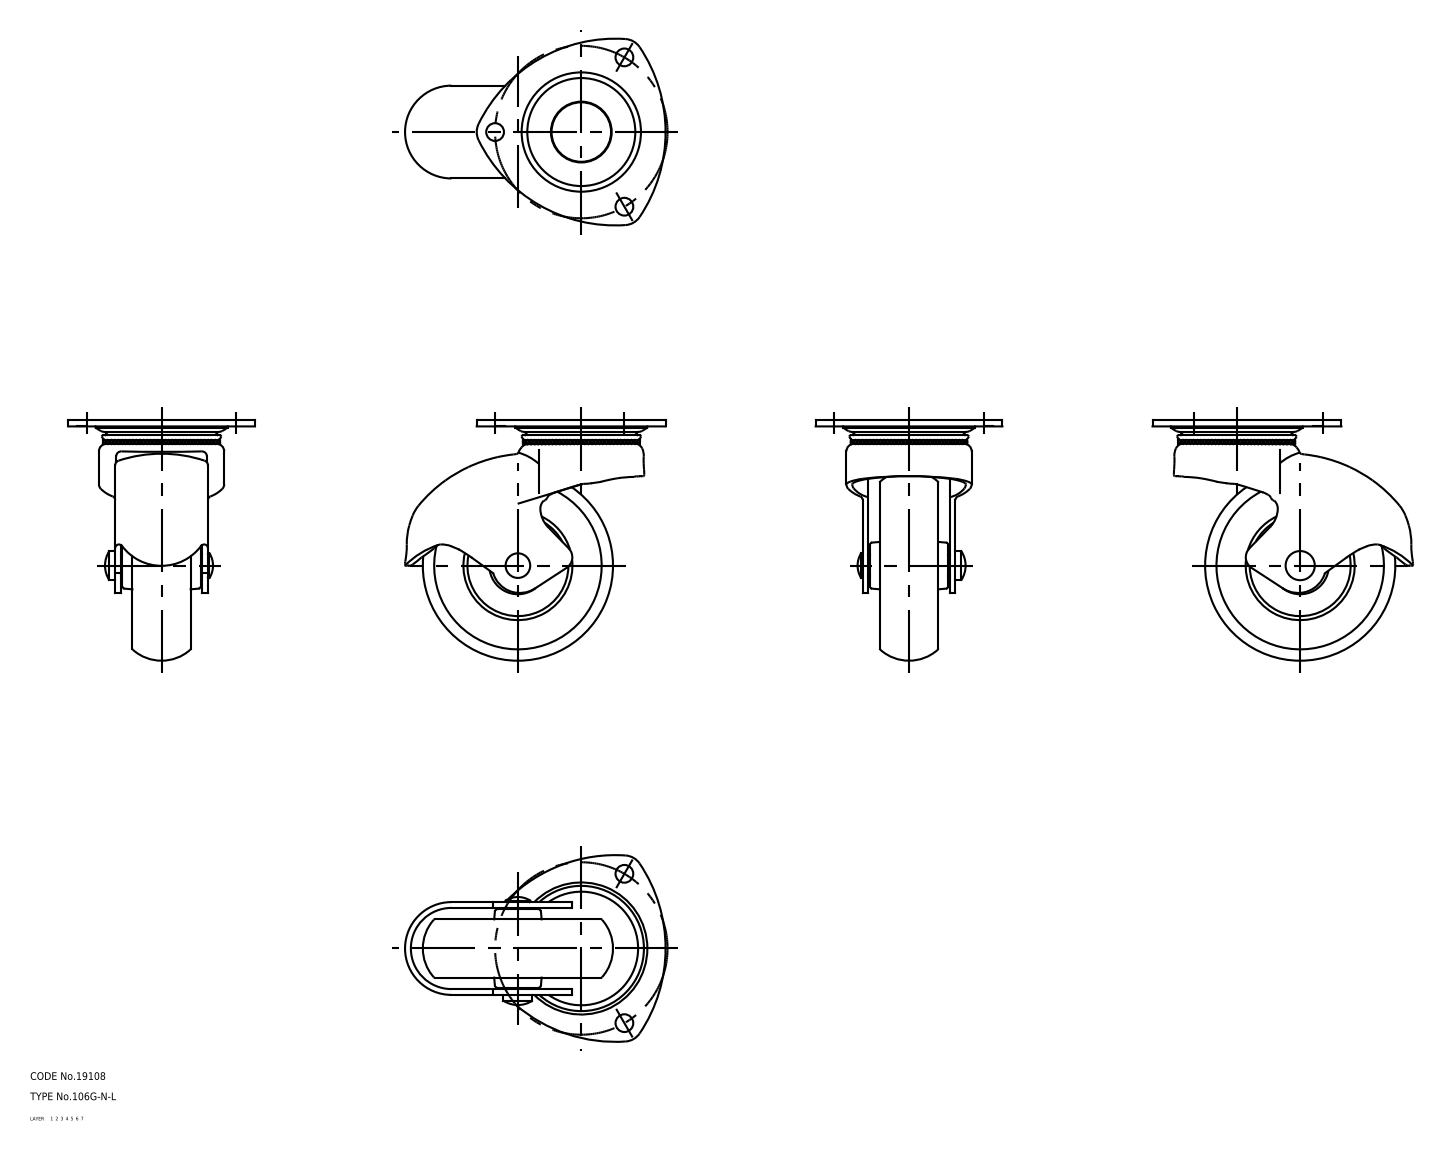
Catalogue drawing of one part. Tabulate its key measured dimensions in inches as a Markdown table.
| quantity | value |
| --- | --- |
| part name | wheel; mounting plate; main shaft; axle (+1 more) |
| STEP written by | CADfix (AUTOMOTIVE_DESIGN) |
| units | inches |
| bodies | 5 solids, 217 faces (0 planar, 0 cylindrical, 217 other) |
| overall size | 4.045 × 3.74 × 2.899 |
| volume | 7.75 in³ |
| surface area | 74.57 in² |
